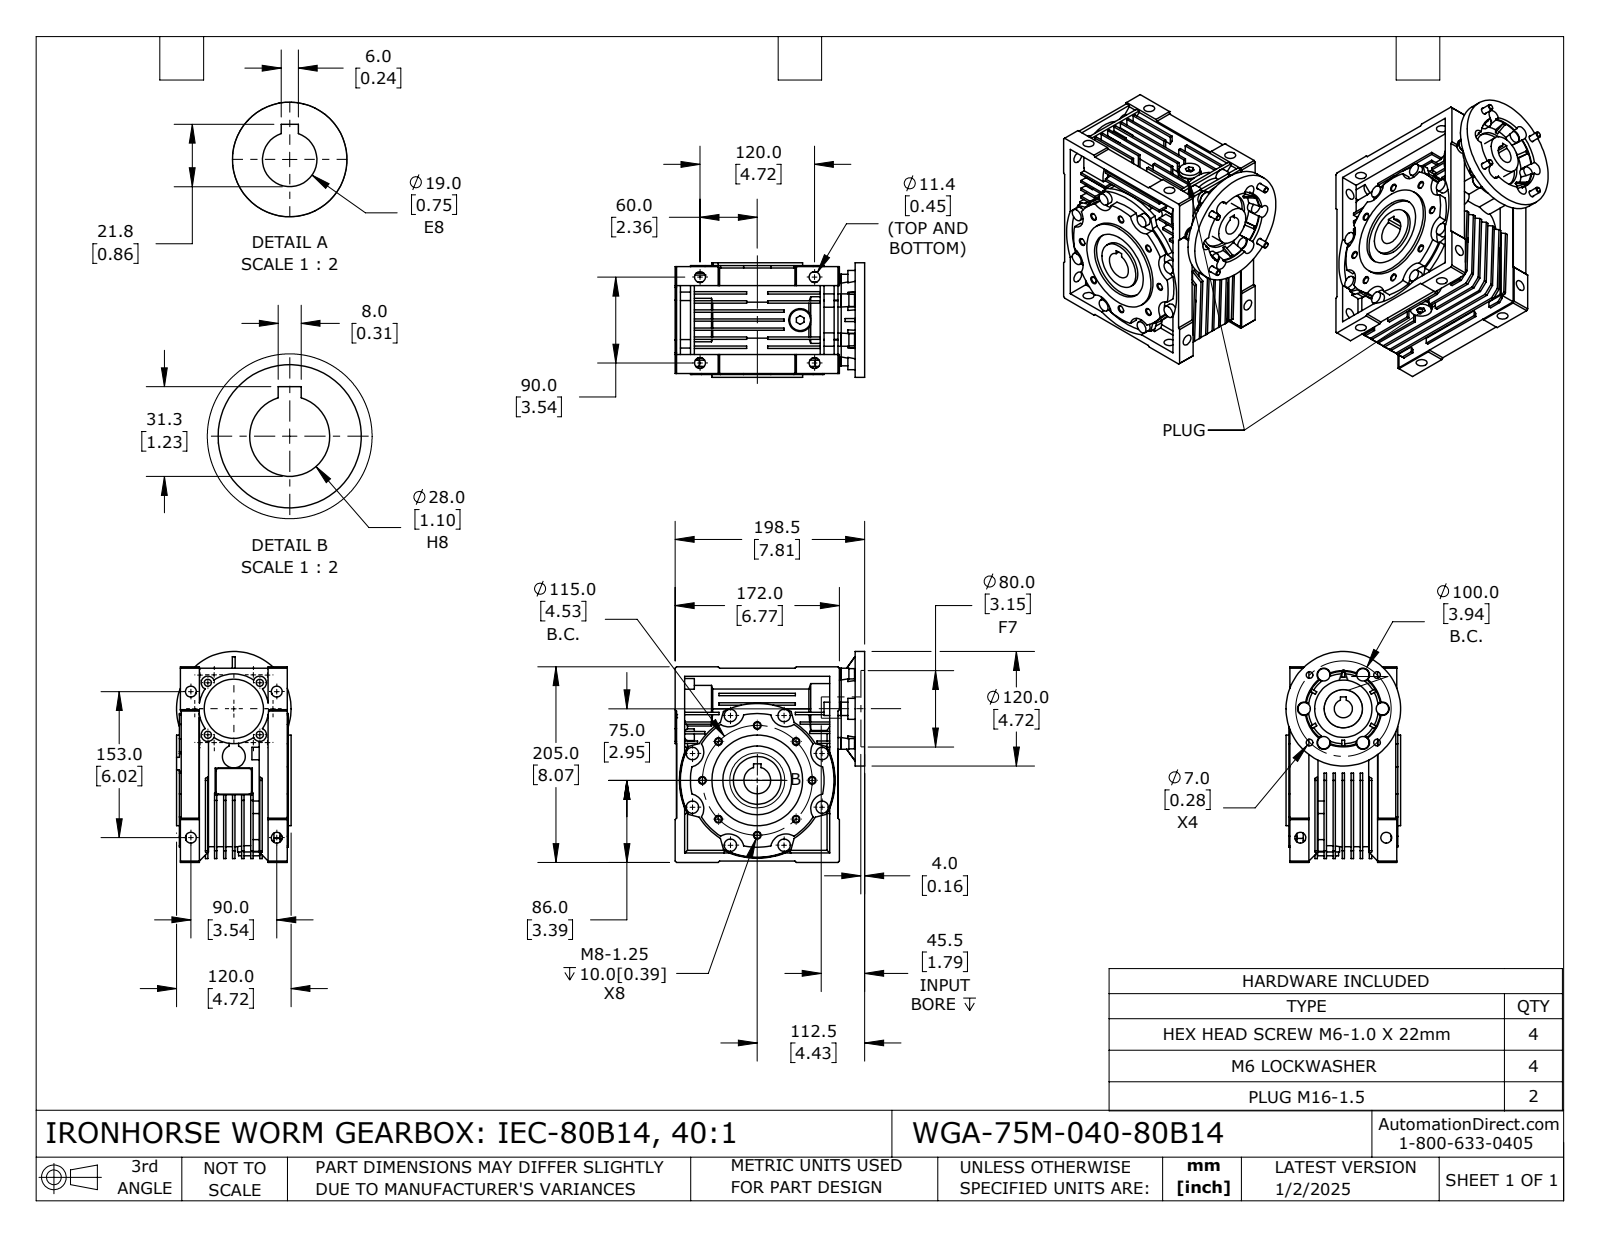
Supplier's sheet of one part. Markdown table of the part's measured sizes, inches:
| quantity | value |
| --- | --- |
| part name | WGA-75M-040-80B14 |
| STEP written by | SolidWorks 2024 (CONFIG_CONTROL_DESIGN) |
| units | inches |
| bodies | 16 solids, 1304 faces (703 planar, 433 cylindrical, 168 other) |
| overall size | 8.701 × 8.228 × 4.724 |
| volume | 174.1 in³ |
| surface area | 745.4 in² |
| round holes (diameter × count) | 0.262 × 8, 0.448 × 8, 0.24 × 4, 0.276 × 4, 0.293 × 4, 0.571 × 2, 0.748 × 1, 0.787 × 1, 1.102 × 1, 1.535 × 1, 1.654 × 1, 1.969 × 1 |
| round bosses / shafts (diameter × count) | 0.512 × 14, 0.48 × 4, 0.236 × 4, 0.945 × 3, 0.866 × 2, 0.622 × 2, 0.539 × 2, 5.509 × 1 |
| partial cylindrical surfaces (radius × count) | 0.276 × 10, 0.63 × 8, 0.433 × 6, 0.098 × 4, 1.417 × 1, 1.437 × 1, 1.535 × 1, 1.575 × 1 |
| main face-to-face distances | 0.374, 0.098, 0.748, 0.472, 0.394, 0.276, 0.65, 1.122, 1.093, 0.846 |
| hole center spacings | 1.733, 2.264, 2.485, 3.202, 4.183, 0.453, 1.515, 1.969 |
